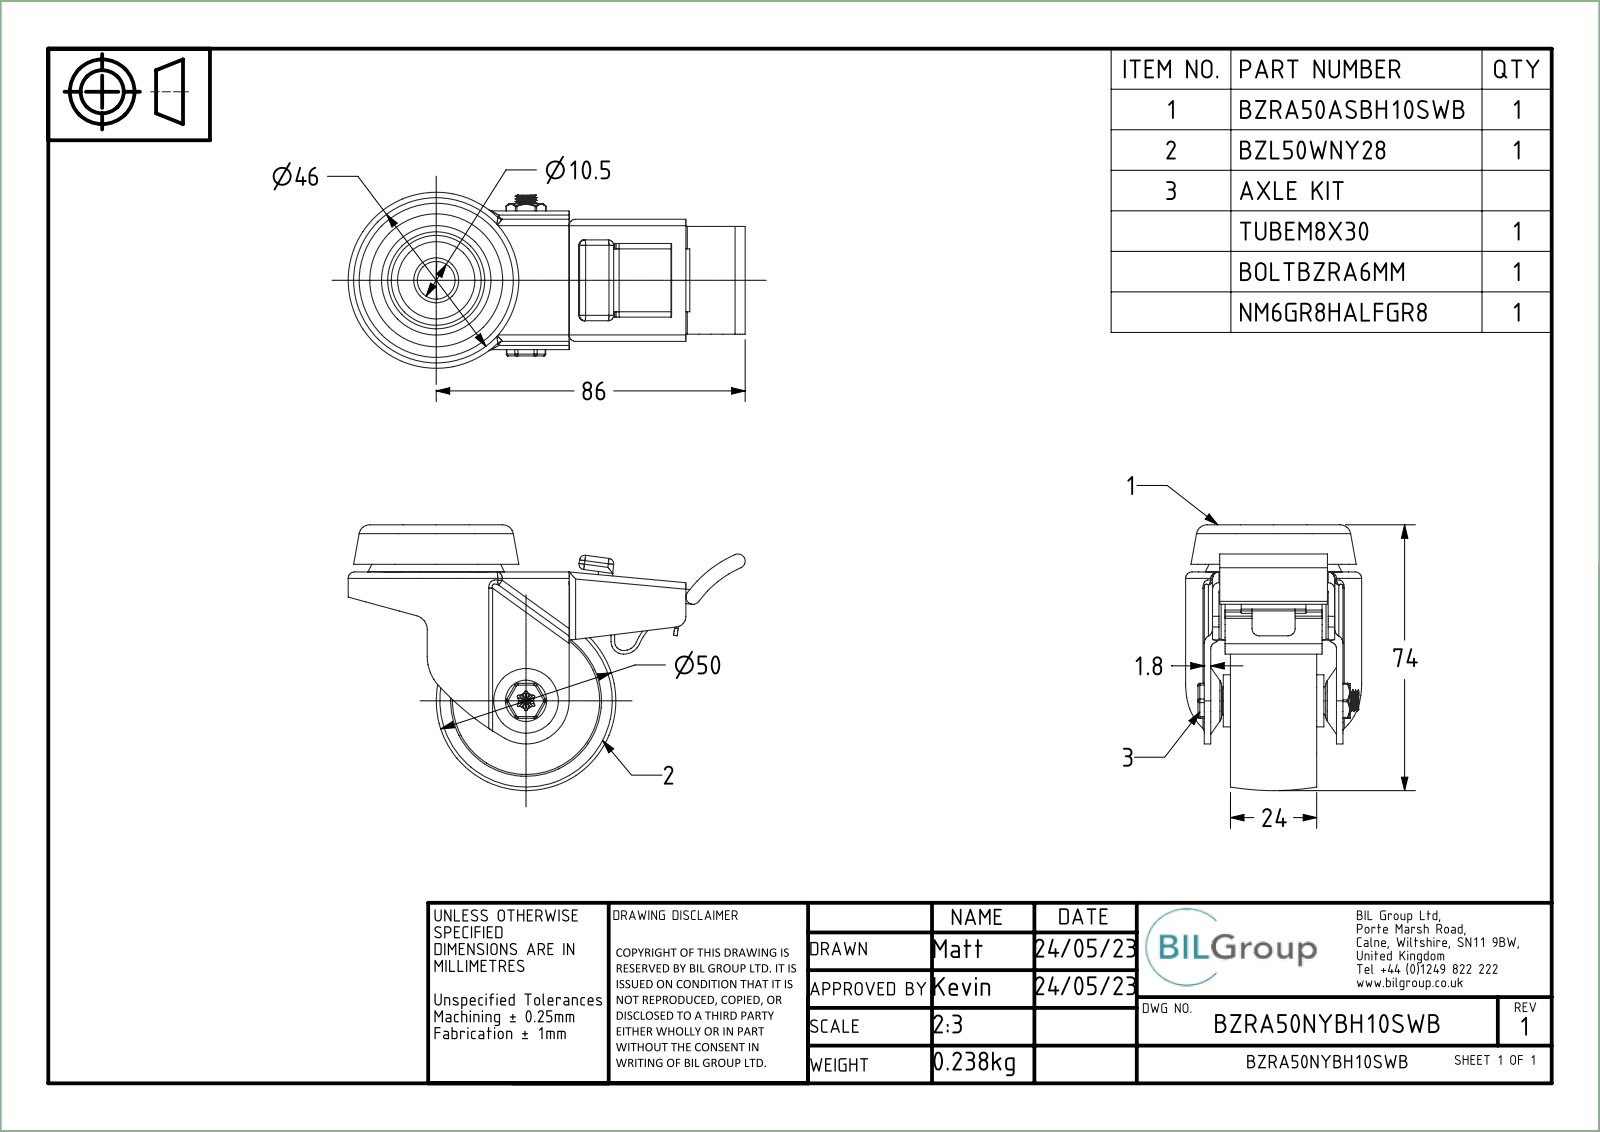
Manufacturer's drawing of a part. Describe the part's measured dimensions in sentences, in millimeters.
The part is named "BZRA50ASBH10SWB; ZINC PLATED PRESSED STEEL FORKS; ZINC PLATED PRESSED STEEL HEAD; ZINC PLATED PRESSED STEEL BRAKE (+8 more)". Its 3-D file was written by "Spatial InterOp 3D (CONFIG_CONTROL_DESIGN)". It is 9 solids with 591 faces: 137 planar, 286 cylindrical and 168 other. Overall it measures 110.5 by 74 by 49 millimeters. Its volume is 51 654 cubic millimeters and its surface area 48 863 square millimeters. Round holes: 1 of diameter 6, 1 of diameter 6.2, 1 of diameter 6.3, 1 of diameter 8.2, 1 of diameter 10.5, 1 of diameter 10.56, 1 of diameter 42. Round bosses or shafts: 1 of diameter 39, 1 of diameter 38, 1 of diameter 18, 1 of diameter 14.76, 1 of diameter 14.5, 1 of diameter 8, 1 of diameter 7.95, 1 of diameter 5. Partial cylindrical surfaces (rounded edges, fillets, slot ends): 28 of radius 1, 22 of radius 1.8, 12 of radius 0.5, 12 of radius 0.9, 11 of radius 1.5, 6 of radius 0.4, 6 of radius 2, 3 of radius 3. The main face-to-face distances are 1.8, 1.81, 3, 3.2, 30.4, 5, 1, 32.2, 13.7, 16.7.
